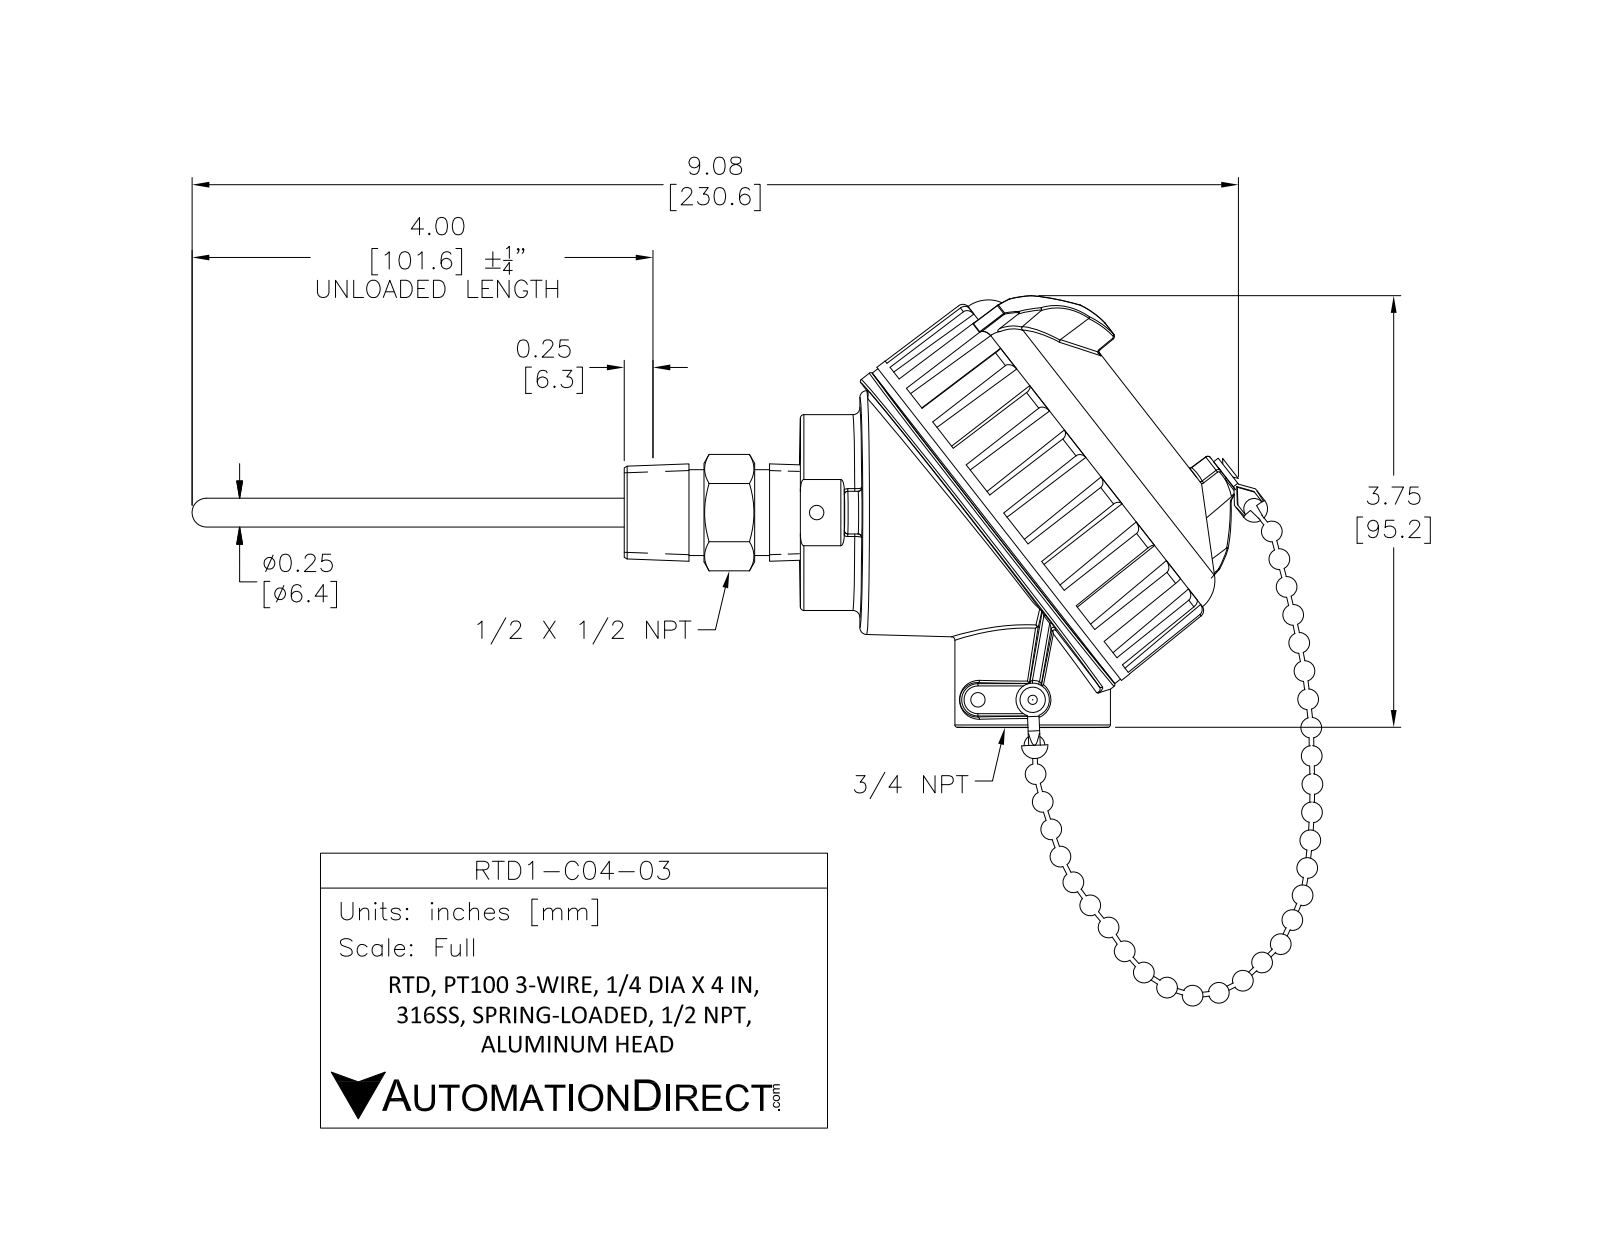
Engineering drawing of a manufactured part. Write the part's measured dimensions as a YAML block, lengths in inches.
part_name: "RTD1-C04-03"
step_written_by: "SolidWorks 2019 (CONFIG_CONTROL_DESIGN)"
units: inches
bodies: {solids: 21, faces: 652, planar: 204, cylindrical: 104, other: 344}
overall_size: [9.225, 4.484, 3.45]
volume: 25.9
surface_area: 115
round_holes:
  - {diameter: 0.08, count: 2}
  - {diameter: 0.125, count: 2}
  - {diameter: 0.144, count: 2}
  - {diameter: 0.04, count: 1}
  - {diameter: 0.165, count: 1}
  - {diameter: 0.25, count: 1}
  - {diameter: 0.688, count: 1}
  - {diameter: 3.005, count: 1}
round_bosses_or_shafts:
  - {diameter: 0.04, count: 3}
  - {diameter: 0.29, count: 2}
  - {diameter: 0.123, count: 2}
  - {diameter: 3.45, count: 1}
  - {diameter: 3.405, count: 1}
  - {diameter: 3.218, count: 1}
  - {diameter: 3.122, count: 1}
  - {diameter: 2.994, count: 1}
partial_cylinders:
  - {radius: 0.02, count: 13}
  - {radius: 0.03, count: 11}
  - {radius: 0.015, count: 7}
  - {radius: 0.064, count: 2}
  - {radius: 0.185, count: 2}
face_to_face_distances: [0.073, 0.063, 0.135, 1.623, 1.56, 1.487, 0.585, 0.875, 1.375, 0.091]
hole_center_spacings: [0.033, 0.475, 0.992, 1, 2.145, 2.481]
